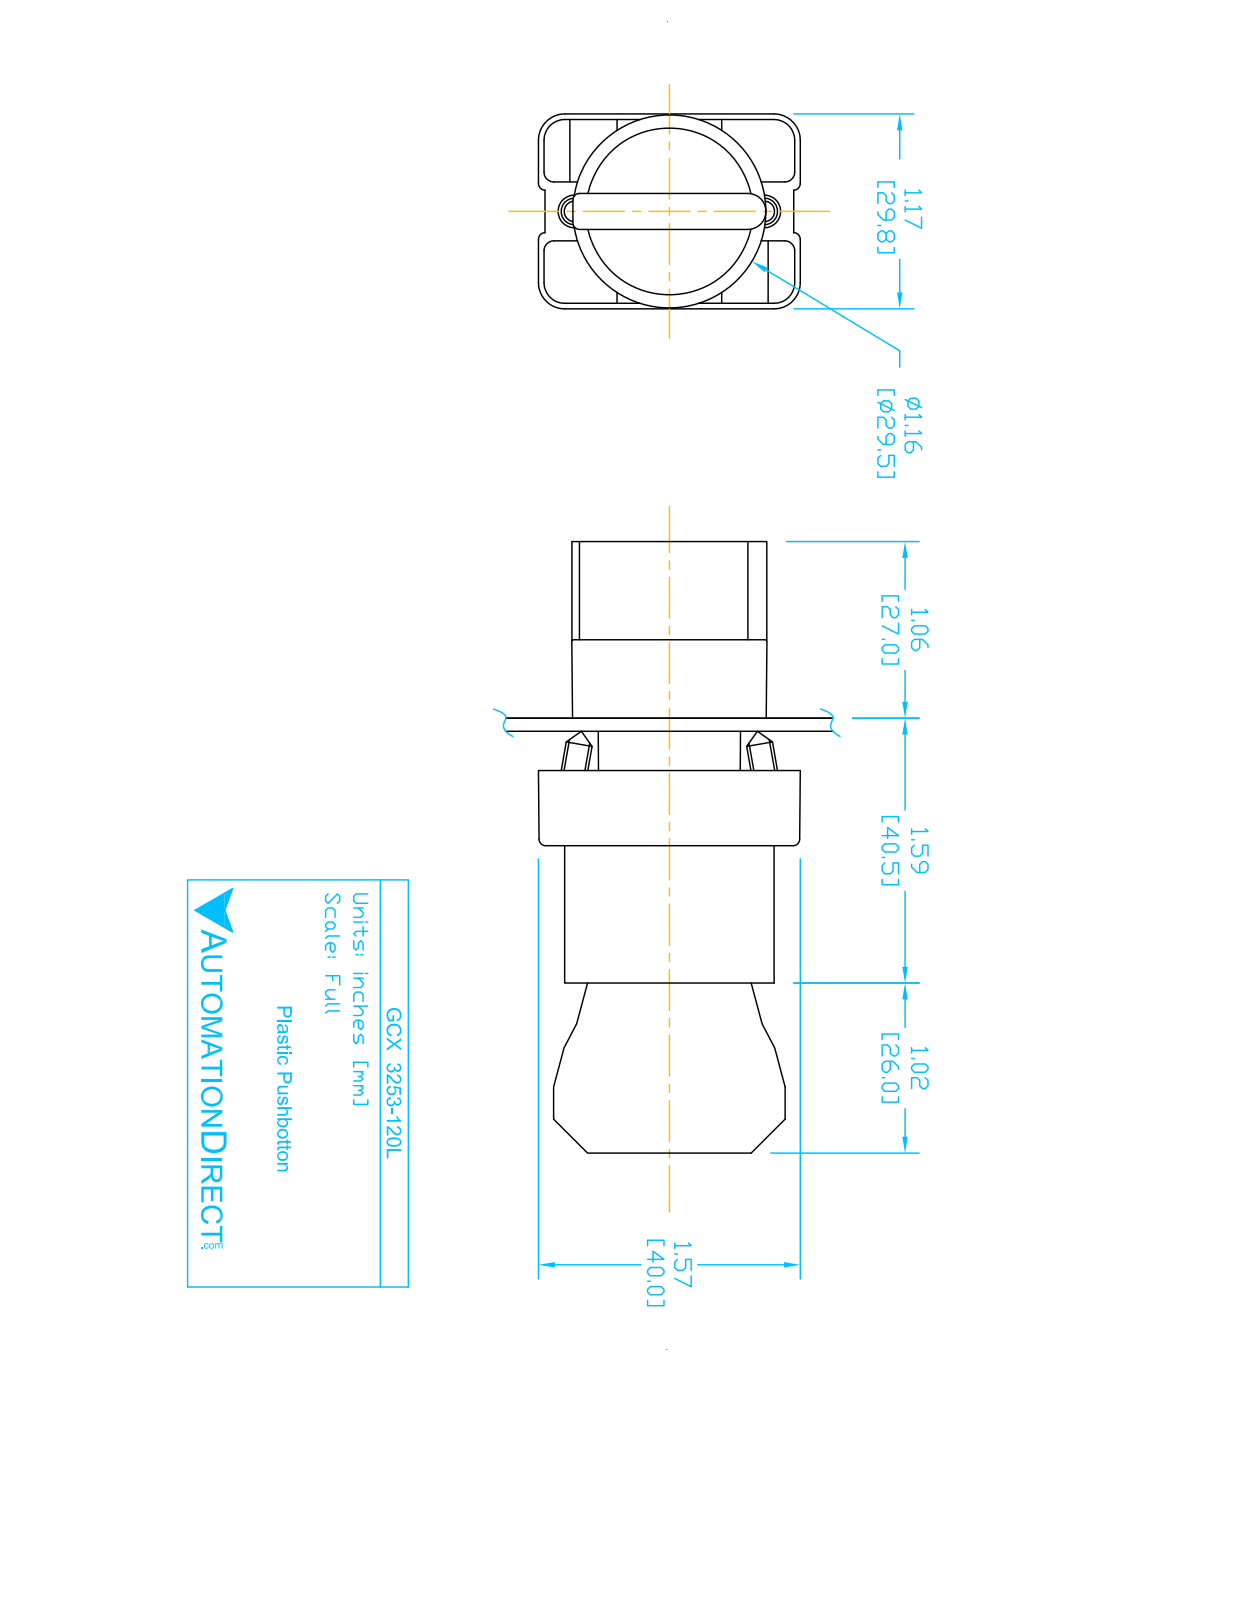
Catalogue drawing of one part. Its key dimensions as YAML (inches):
part_name: "ECX3029-2; ECX1050; GCX3253-120L; ecx1040 (+1 more)"
step_written_by: "SolidWorks 2016 (AUTOMOTIVE_DESIGN)"
units: inches
bodies: {solids: 8, faces: 445, planar: 263, cylindrical: 151, other: 31}
overall_size: [3.653, 1.581, 1.177]
volume: 2.799
surface_area: 39
round_holes:
  - {diameter: 0.079, count: 2}
  - {diameter: 0.124, count: 2}
  - {diameter: 0.13, count: 2}
  - {diameter: 0.087, count: 1}
  - {diameter: 0.197, count: 1}
  - {diameter: 0.469, count: 1}
  - {diameter: 0.878, count: 1}
  - {diameter: 0.888, count: 1}
  - {diameter: 1.024, count: 1}
round_bosses_or_shafts:
  - {diameter: 0.157, count: 4}
  - {diameter: 1.175, count: 1}
  - {diameter: 1.004, count: 1}
  - {diameter: 0.945, count: 1}
  - {diameter: 0.856, count: 1}
  - {diameter: 0.78, count: 1}
  - {diameter: 0.504, count: 1}
partial_cylinders:
  - {radius: 0.059, count: 24}
  - {radius: 0.041, count: 12}
  - {radius: 0.124, count: 12}
  - {radius: 0.157, count: 12}
  - {radius: 0.039, count: 9}
  - {radius: 0.128, count: 2}
  - {radius: 0.02, count: 1}
  - {radius: 0.063, count: 1}
face_to_face_distances: [0.827, 2.02, 1.193, 0.579, 1.244, 1.171, 0.472, 0.469, 0.031, 0.033]
hole_center_spacings: [0.236, 0.544, 0.472, 0.49]
